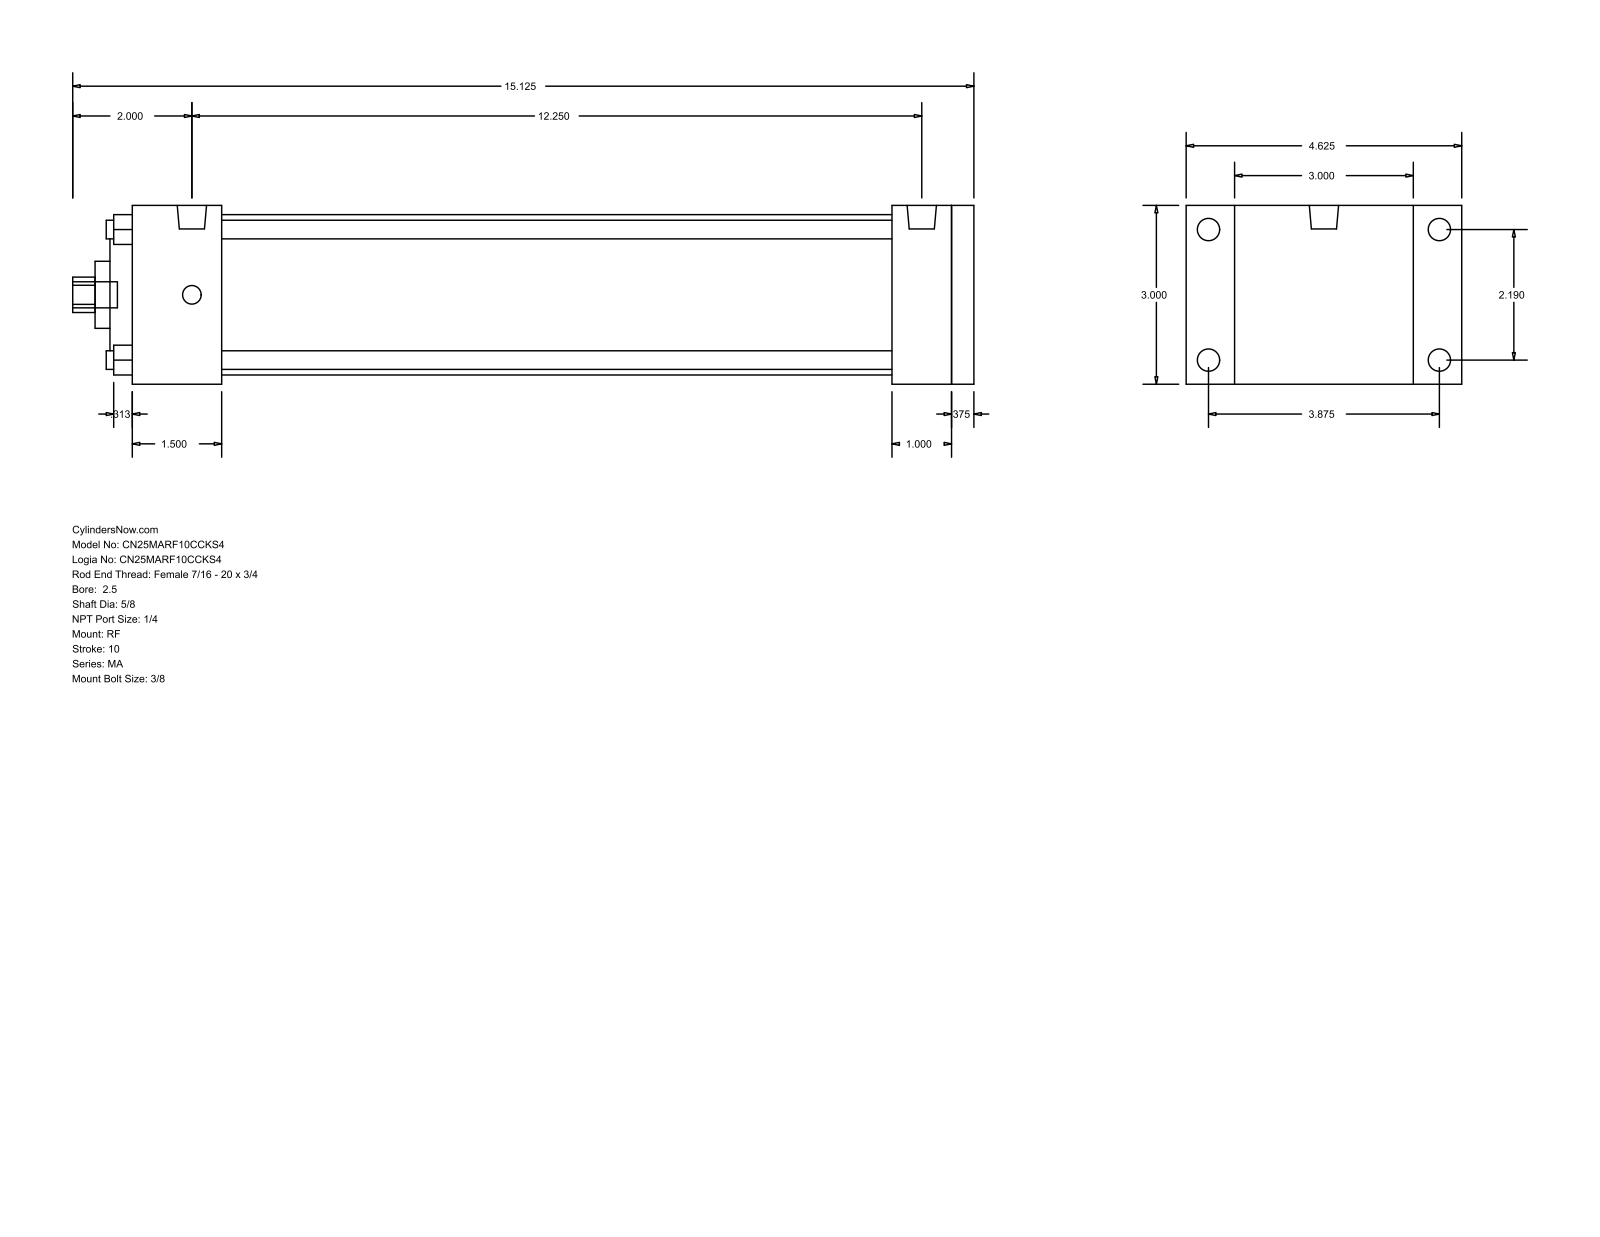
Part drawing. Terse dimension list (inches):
name: MA_RF__0250_0.625
written by: GSSL Pune (CONFIG_CONTROL_DESIGN)
unit: in
bodies: 0 solids, 94 faces (65 planar, 29 cylindrical, 0 other)
size: 15.125 × 4.625 × 3
holes: 4× ⌀0.313, 1× ⌀0.625, 1× ⌀1.125, 1× ⌀2, 1× ⌀2.69
bosses: 4× ⌀0.375, 4× ⌀0.313, 2× ⌀0.492, 1× ⌀0.437
rounds: 1× R0.297
face distances: 3, 14.125, 0.375, 13.75, 1, 1.5, 12.75, 11.25, 12.25, 12.625
hole spacings: 1.548, 2.19, 3.097
